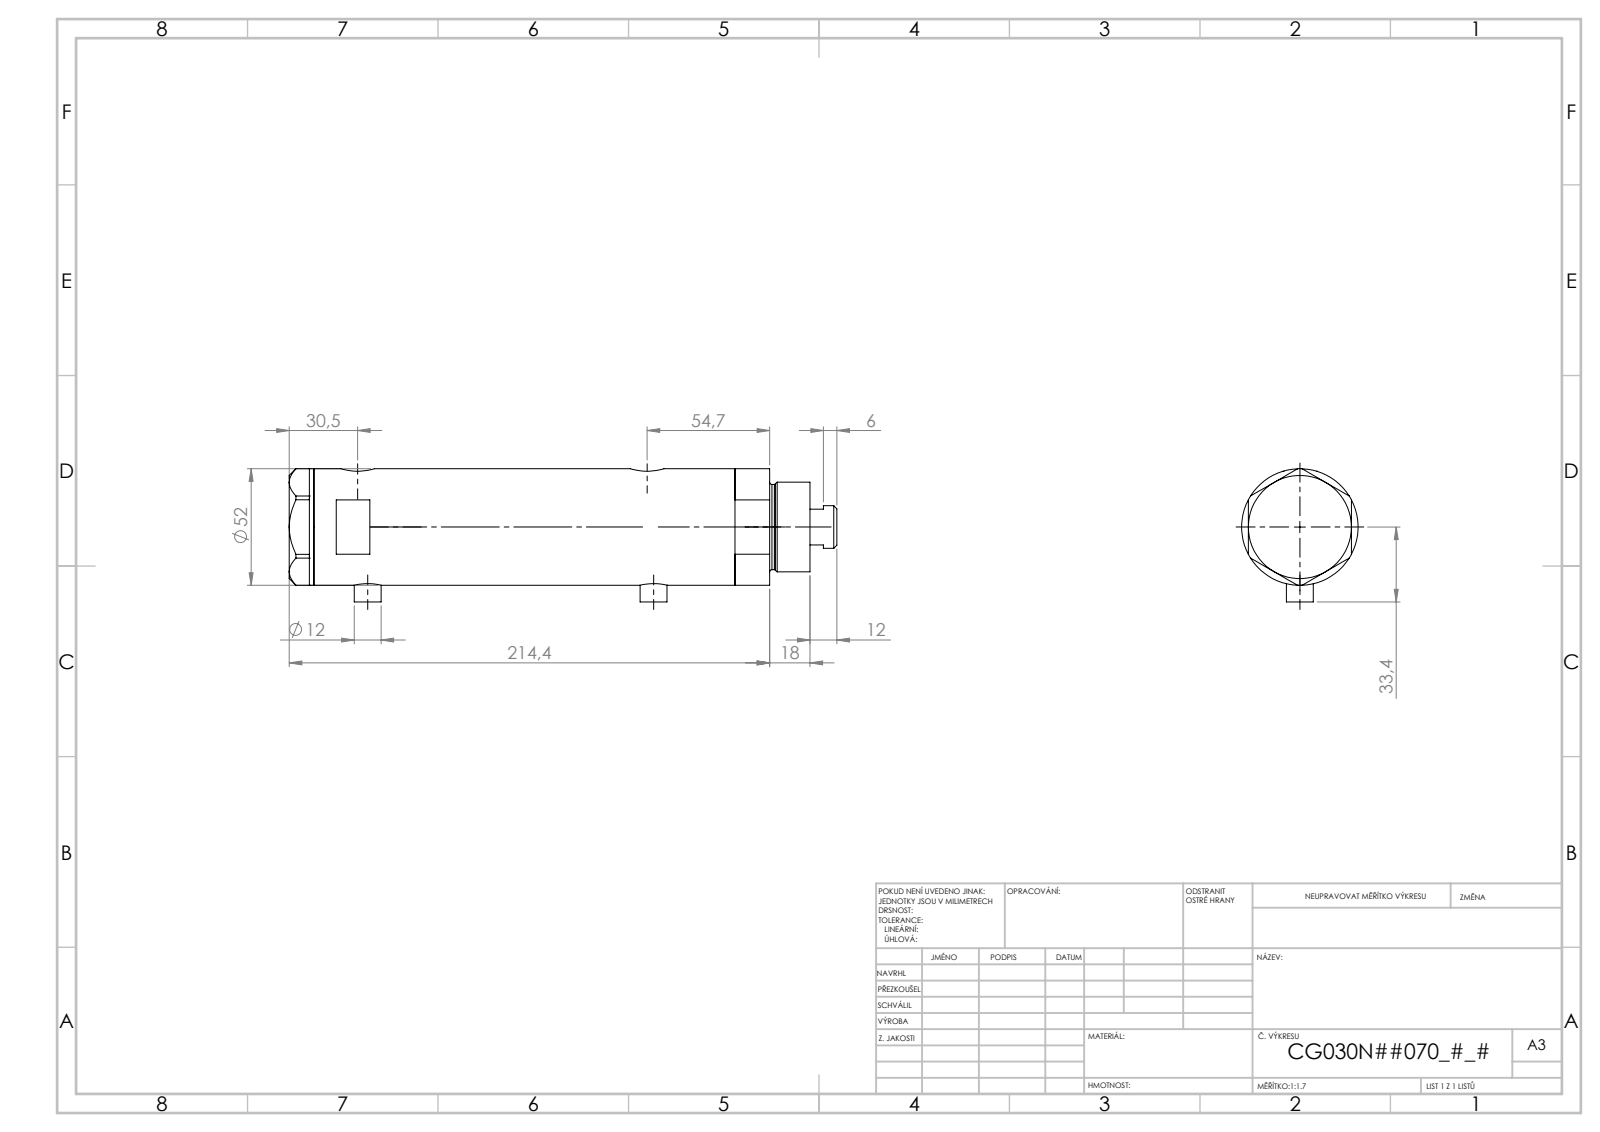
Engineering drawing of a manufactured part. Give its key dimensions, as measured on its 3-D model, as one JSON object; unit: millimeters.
{"part_name": "V270CG_BACK; V270CG_MIDDLE; V270CG_VC; V270CG_FRONT", "step_written_by": "SolidWorks 2019 (CONFIG_CONTROL_DESIGN)", "units": "millimeters", "bodies": {"solids": 4, "faces": 140, "planar": 67, "cylindrical": 53, "other": 20}, "overall_size": [219.02, 53.1, 52], "volume_mm3": 388690, "surface_area_mm2": 87520, "round_holes": [[5, 2], [9.73, 2], [12.5, 2], [15, 2], [6.5, 1], [20, 1], [21.5, 1], [30, 1], [33, 1], [44, 1]], "round_bosses_or_shafts": [[12, 2], [52, 1], [40, 1], [38, 1], [19, 1]], "face_to_face_distances": [123.54, 23.8, 99.74, 11, 34.8, 134.54, 46, 170.94, 159.94, 136.14], "hole_center_spacings": [2.9, 4.5, 96.75, 99.65, 101.25, 104.15, 2.89, 2.91]}
